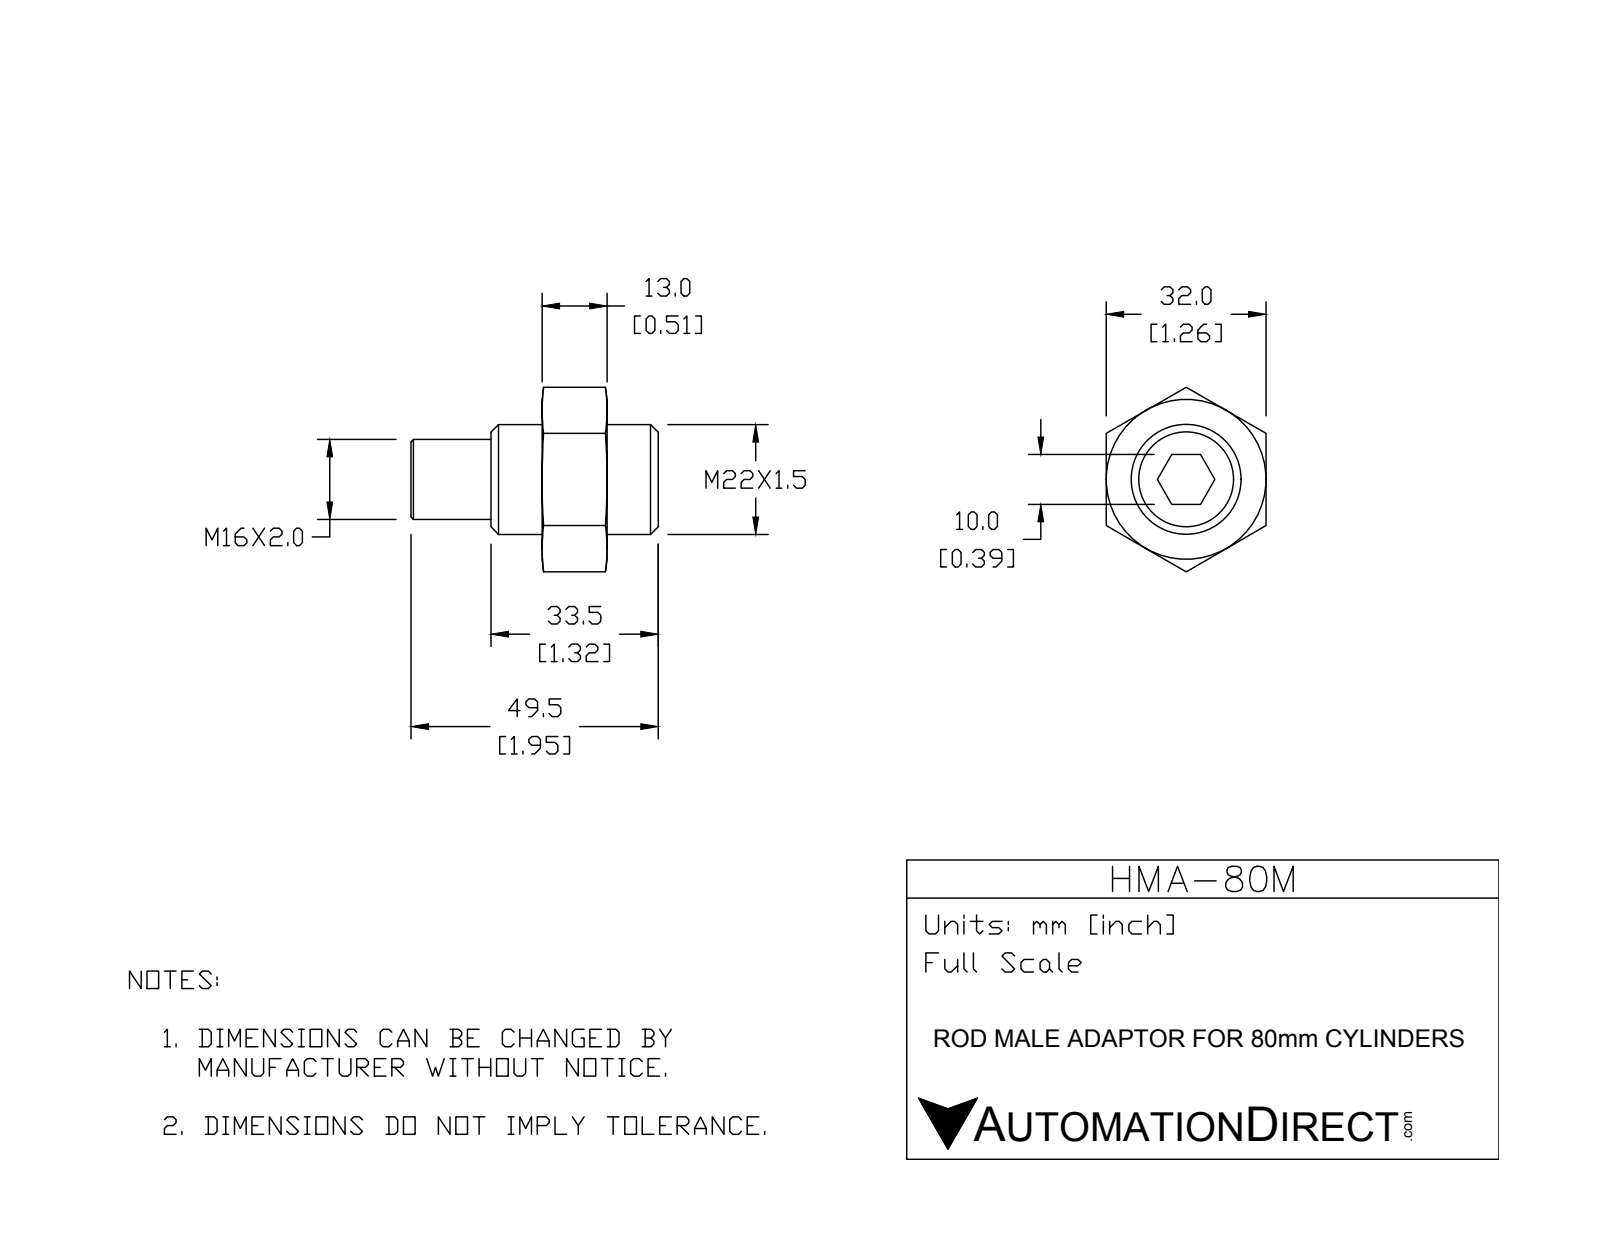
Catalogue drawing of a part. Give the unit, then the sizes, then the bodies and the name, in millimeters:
Units: millimetres
Overall size (bounding box): 49.5 × 36.95 × 32
Round holes (diameter × count): ⌀22 ×1
Round bosses / shafts (diameter × count): ⌀16 ×1
Main face-to-face distances: 32, 13, 10.25, 23.25, 49.5, 39.25, 26.25, 10.24, 9, 1.25
Volume: 21 544 mm³ · Surface area: 7 386 mm²
Bodies: 2 solids, 44 faces (18 planar, 6 cylindrical, 20 other)
Part name (STEP PRODUCT): HMA-80M
STEP written by: SolidWorks 2015 (CONFIG_CONTROL_DESIGN)
